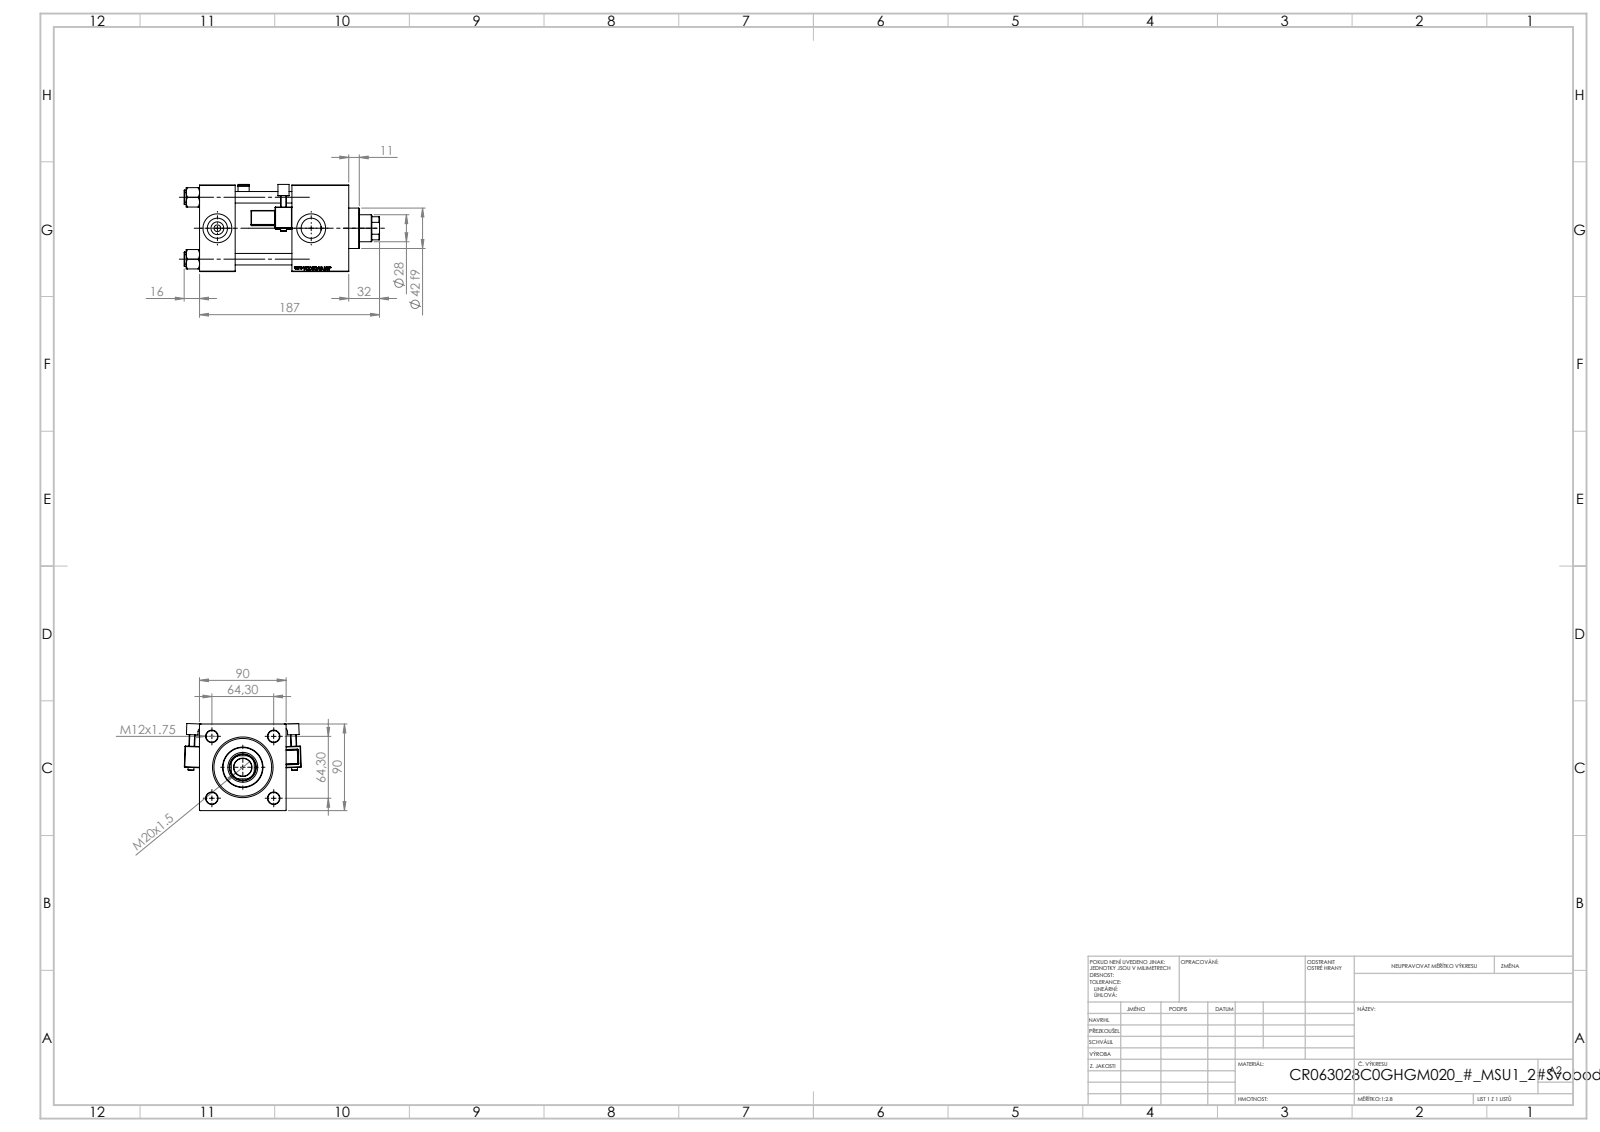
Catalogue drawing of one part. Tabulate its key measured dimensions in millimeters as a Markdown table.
| quantity | value |
| --- | --- |
| part name | V215CR_C_Body; V215CR_C_TYCINKA; NUT_M5_C; V215CR_MSU (+2 more) |
| STEP written by | SolidWorks 2019 (CONFIG_CONTROL_DESIGN) |
| units | millimeters |
| bodies | 13 solids, 1302 faces (584 planar, 146 cylindrical, 572 other) |
| overall size | 203 × 121.57 × 90.53 |
| volume | 988 032 mm³ |
| surface area | 191 397 mm² |
| round holes (diameter × count) | 12 × 4, 7 × 2, 20.96 × 2, 30 × 2, 18.5 × 1, 28 × 1, 31 × 1, 50 × 1, 60 × 1, 63 × 1 |
| round bosses / shafts (diameter × count) | 15 × 4, 6 × 2, 69 × 1, 42 × 1 |
| partial cylindrical surfaces (radius × count) | 0.5 × 48, 1 × 2, 2.5 × 2, 4 × 2, 13.5 × 1 |
| main face-to-face distances | 90, 59, 37, 155, 118, 96, 126.3, 89.3, 30.3, 28.7 |
| hole center spacings | 45.47, 64.3, 90.93, 97.5 |
